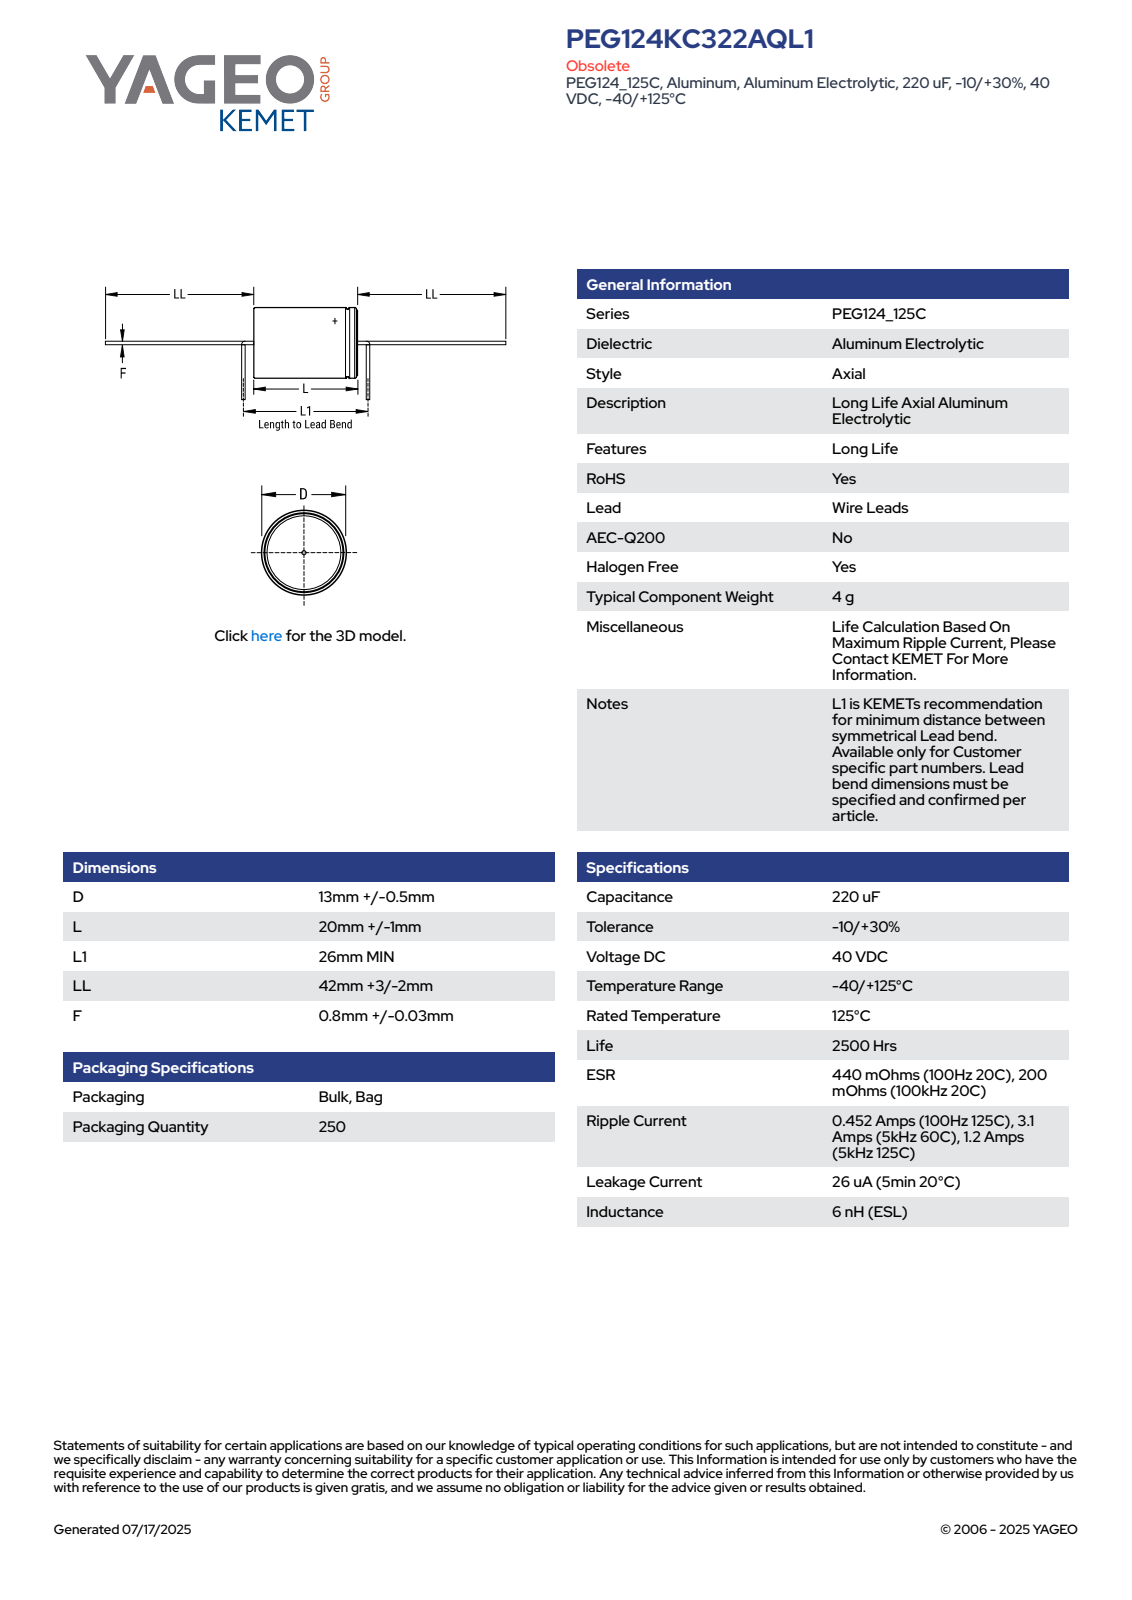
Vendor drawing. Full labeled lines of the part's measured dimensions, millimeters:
Part name (STEP PRODUCT): CAA_PEG124_13X20_D13.5L21LL45F0.83
STEP written by: SolidWorks 2014 (AUTOMOTIVE_DESIGN)
Units: millimetres
Bodies: 1 solid, 99 faces (27 planar, 29 cylindrical, 43 other)
Overall size (bounding box): 108 × 13.5 × 13.5
Volume: 2 924 mm³ · Surface area: 1 448 mm²
Round holes (diameter × count): ⌀12.5 ×1
Round bosses / shafts (diameter × count): ⌀13.5 ×1, ⌀13 ×1, ⌀0.83 ×1
Partial cylindrical surfaces — rounded edges, fillets, slot ends (radius × count): R6.74 ×1
Main face-to-face distances: 20, 21, 1, 45, 65, 66, 108, 63, 43, 42
